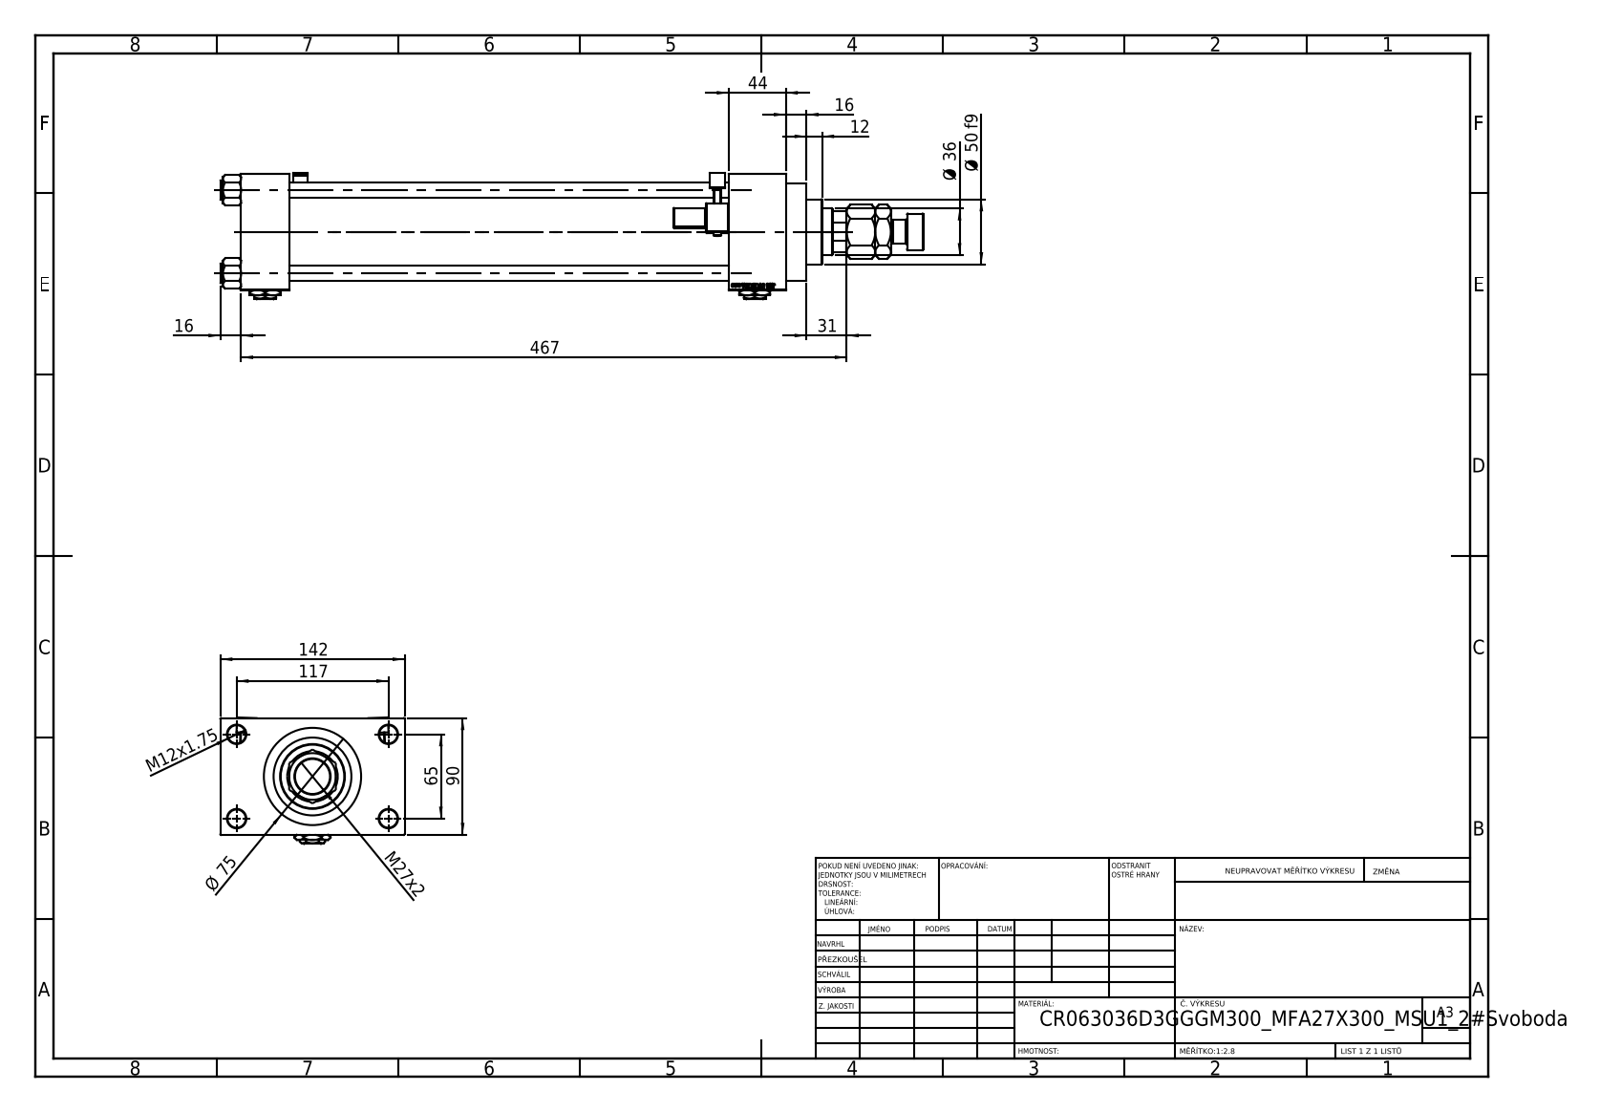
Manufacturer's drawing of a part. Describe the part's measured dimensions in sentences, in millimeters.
The part is named "V215_VC_A; NUT_M5_D; V215CR_MSU; MFA (+4 more)". Its 3-D file was written by "SolidWorks 2019 (CONFIG_CONTROL_DESIGN)". It is 16 solids with 1411 faces: 619 planar, 164 cylindrical and 628 other. Overall it measures 542 by 142 by 97.53 millimeters. Its volume is 1 790 000 cubic millimeters and its surface area 419 776 square millimeters. Round holes: 4 of diameter 12, 4 of diameter 14, 2 of diameter 7, 2 of diameter 20.96, 2 of diameter 30, 1 of diameter 25.5, 1 of diameter 36, 1 of diameter 39, 1 of diameter 50, 1 of diameter 60, 1 of diameter 63. Round bosses or shafts: 4 of diameter 15, 2 of diameter 6, 1 of diameter 75, 1 of diameter 69, 1 of diameter 28, 1 of diameter 18. Partial cylindrical surfaces (rounded edges, fillets, slot ends): 48 of radius 0.5, 2 of radius 1, 2 of radius 2.5, 2 of radius 4, 1 of radius 17.5. The main face-to-face distances are 90, 339, 37, 376, 420, 383, 44, 26, 116, 142. The hole center spacings are 26.35, 45.47, 64.3, 66.92, 69.81, 90.65, 111.34, 65.
